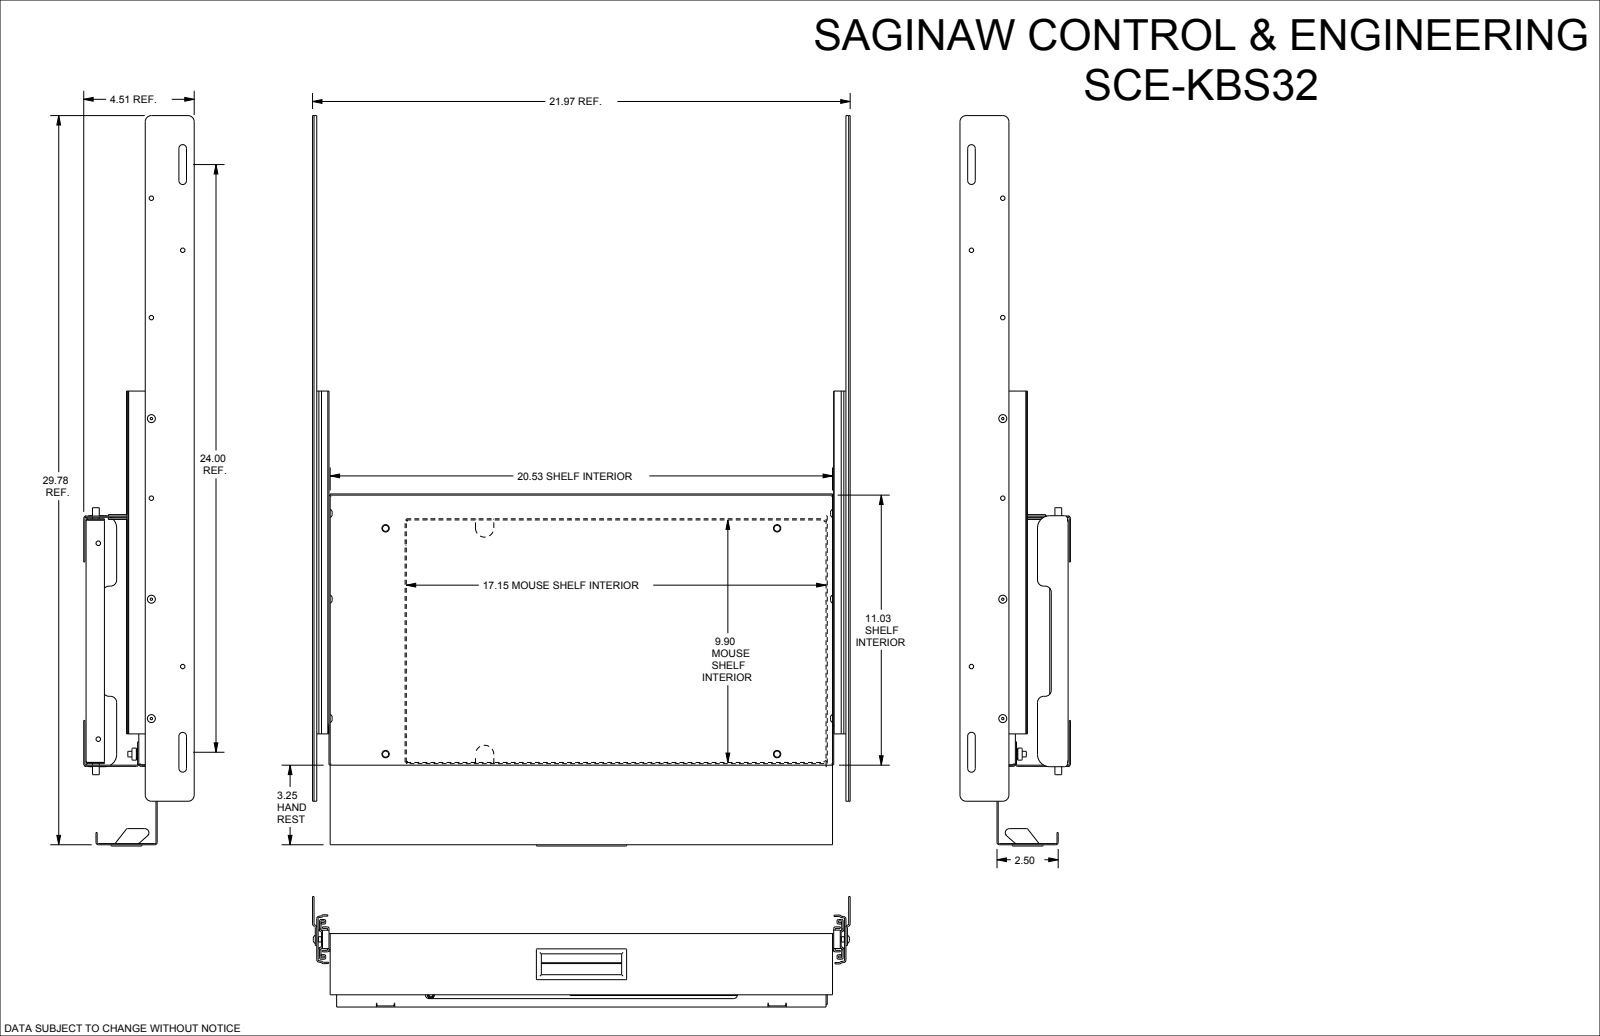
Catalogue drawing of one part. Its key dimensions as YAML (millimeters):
part_name: "SCE-KBS32"
step_written_by: "SolidWorks 2019 (AUTOMOTIVE_DESIGN)"
units: millimeters
bodies: {solids: 32, faces: 956, planar: 485, cylindrical: 397, other: 74}
overall_size: [757.7, 558, 114.7]
volume: 1289000
surface_area: 1548000
round_holes:
  - {diameter: 5.1, count: 22}
  - {diameter: 4.6, count: 8}
  - {diameter: 2.5, count: 6}
  - {diameter: 4, count: 6}
  - {diameter: 6.4, count: 4}
  - {diameter: 7.9, count: 4}
  - {diameter: 4.7, count: 2}
  - {diameter: 4, count: 1}
  - {diameter: 7.1, count: 1}
  - {diameter: 22.2, count: 1}
  - {diameter: 22.2, count: 1}
round_bosses_or_shafts:
  - {diameter: 5.5, count: 6}
  - {diameter: 4.1, count: 6}
  - {diameter: 7.6, count: 4}
  - {diameter: 5.8, count: 4}
  - {diameter: 7.1, count: 1}
partial_cylinders:
  - {radius: 0.8, count: 20}
  - {radius: 1.6, count: 16}
  - {radius: 6.4, count: 16}
  - {radius: 0.8, count: 15}
  - {radius: 2.4, count: 11}
  - {radius: 1.2, count: 10}
  - {radius: 1.5, count: 9}
  - {radius: 0.2, count: 8}
face_to_face_distances: [1.2, 1.3, 54.7, 53.5, 54.7, 56, 2.4, 17.8, 57.2, 7.6]
hole_center_spacings: [12.7, 273.1, 25.4, 260.4, 311.2, 73, 88.9, 98.4]
